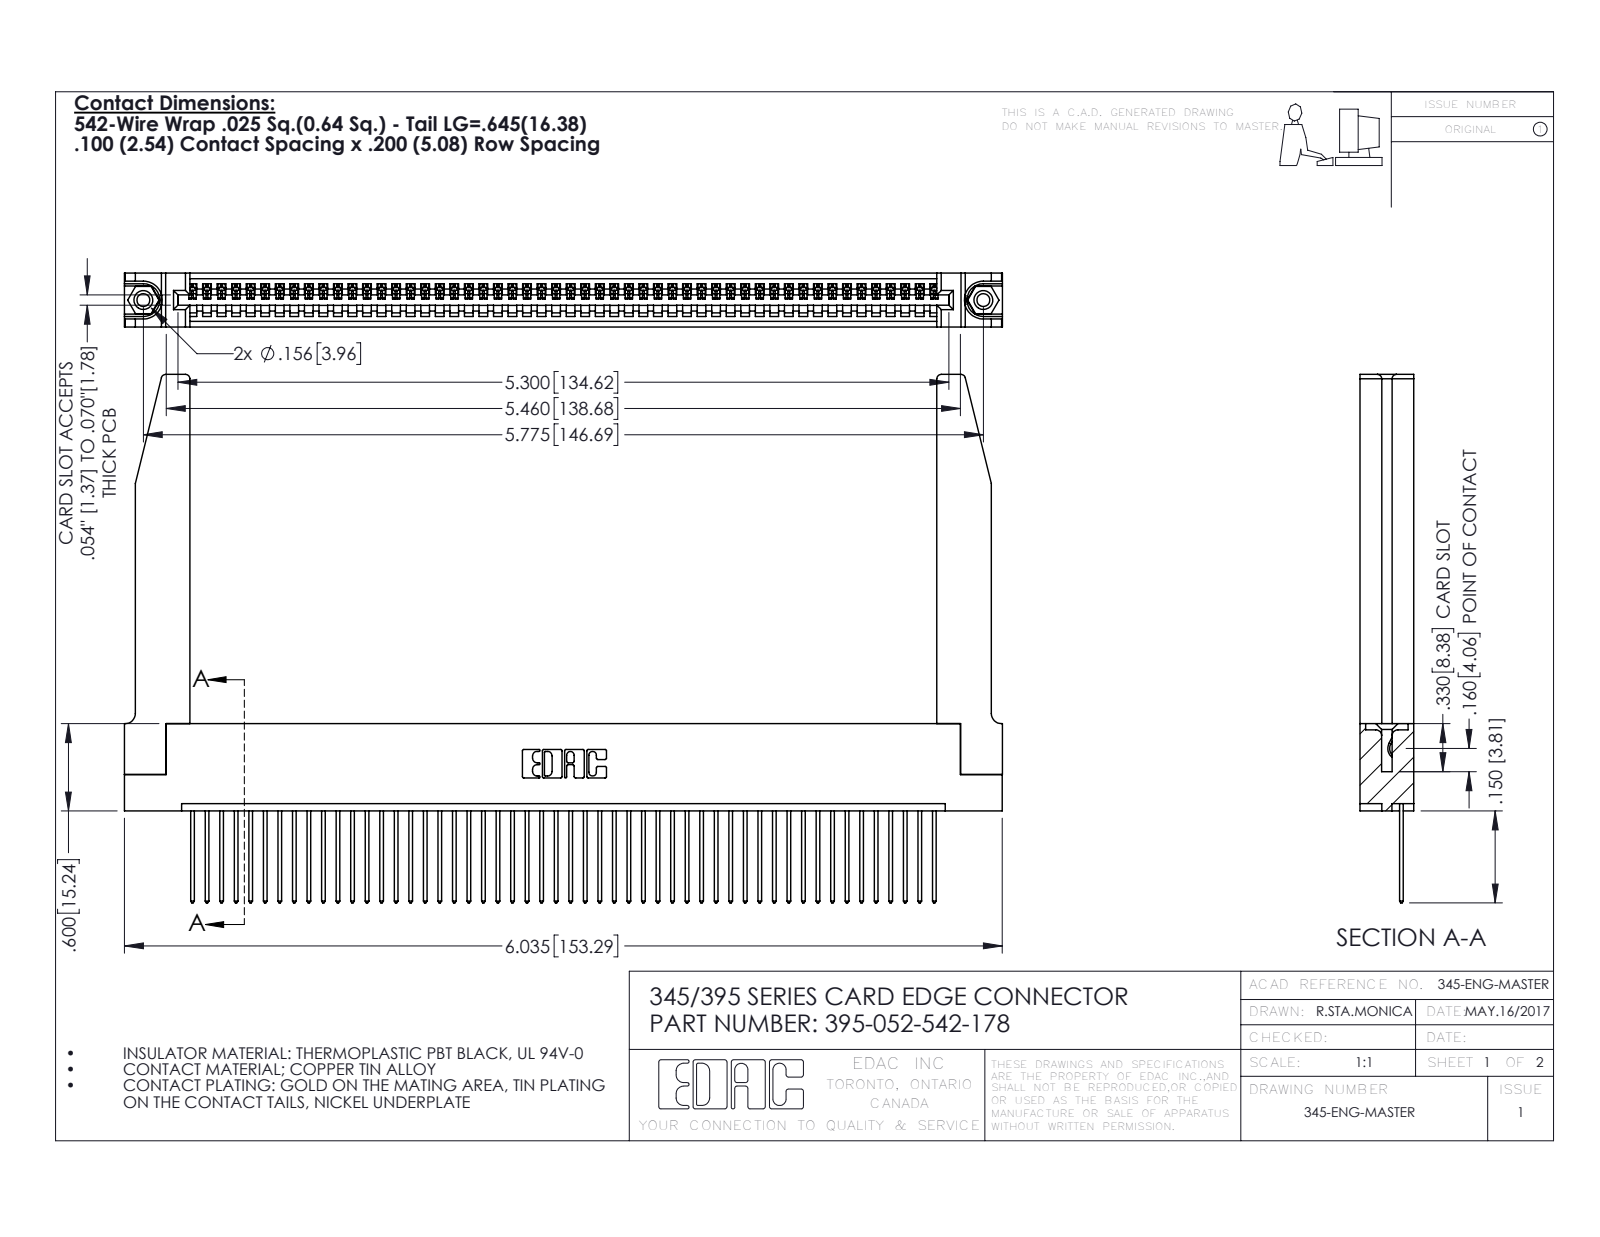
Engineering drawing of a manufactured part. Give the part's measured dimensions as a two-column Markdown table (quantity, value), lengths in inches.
| quantity | value |
| --- | --- |
| part name | 345 Part_Flush Mounting Lugs - 0.156 Dia-TH; 345-292-001_345-293-142; 395-052-542-178; 345-250-001_345-250-001-102 (+1 more) |
| STEP written by | SolidWorks 2016 (CONFIG_CONTROL_DESIGN) |
| units | inches |
| bodies | 57 solids, 3376 faces (2302 planar, 1022 cylindrical, 52 other) |
| overall size | 6.036 × 3.632 × 0.37 |
| volume | 1.375 in³ |
| surface area | 42.36 in² |
| round holes (diameter × count) | 0.089 × 2, 0.125 × 2, 0.156 × 2, 0.064 × 1 |
| round bosses / shafts (diameter × count) | 0.155 × 2 |
| partial cylindrical surfaces (radius × count) | 0.006 × 104, 0.01 × 104, 0.01 × 22, 0.03 × 8, 0.007 × 6, 0.031 × 6, 0.026 × 3, 0.031 × 2 |
| main face-to-face distances | 0.072, 0.37, 0.298, 0.098, 0.272, 0.025, 0.2, 0.225, 0.15, 0.148 |
| hole center spacings | 0.27, 5.539, 5.775 |
